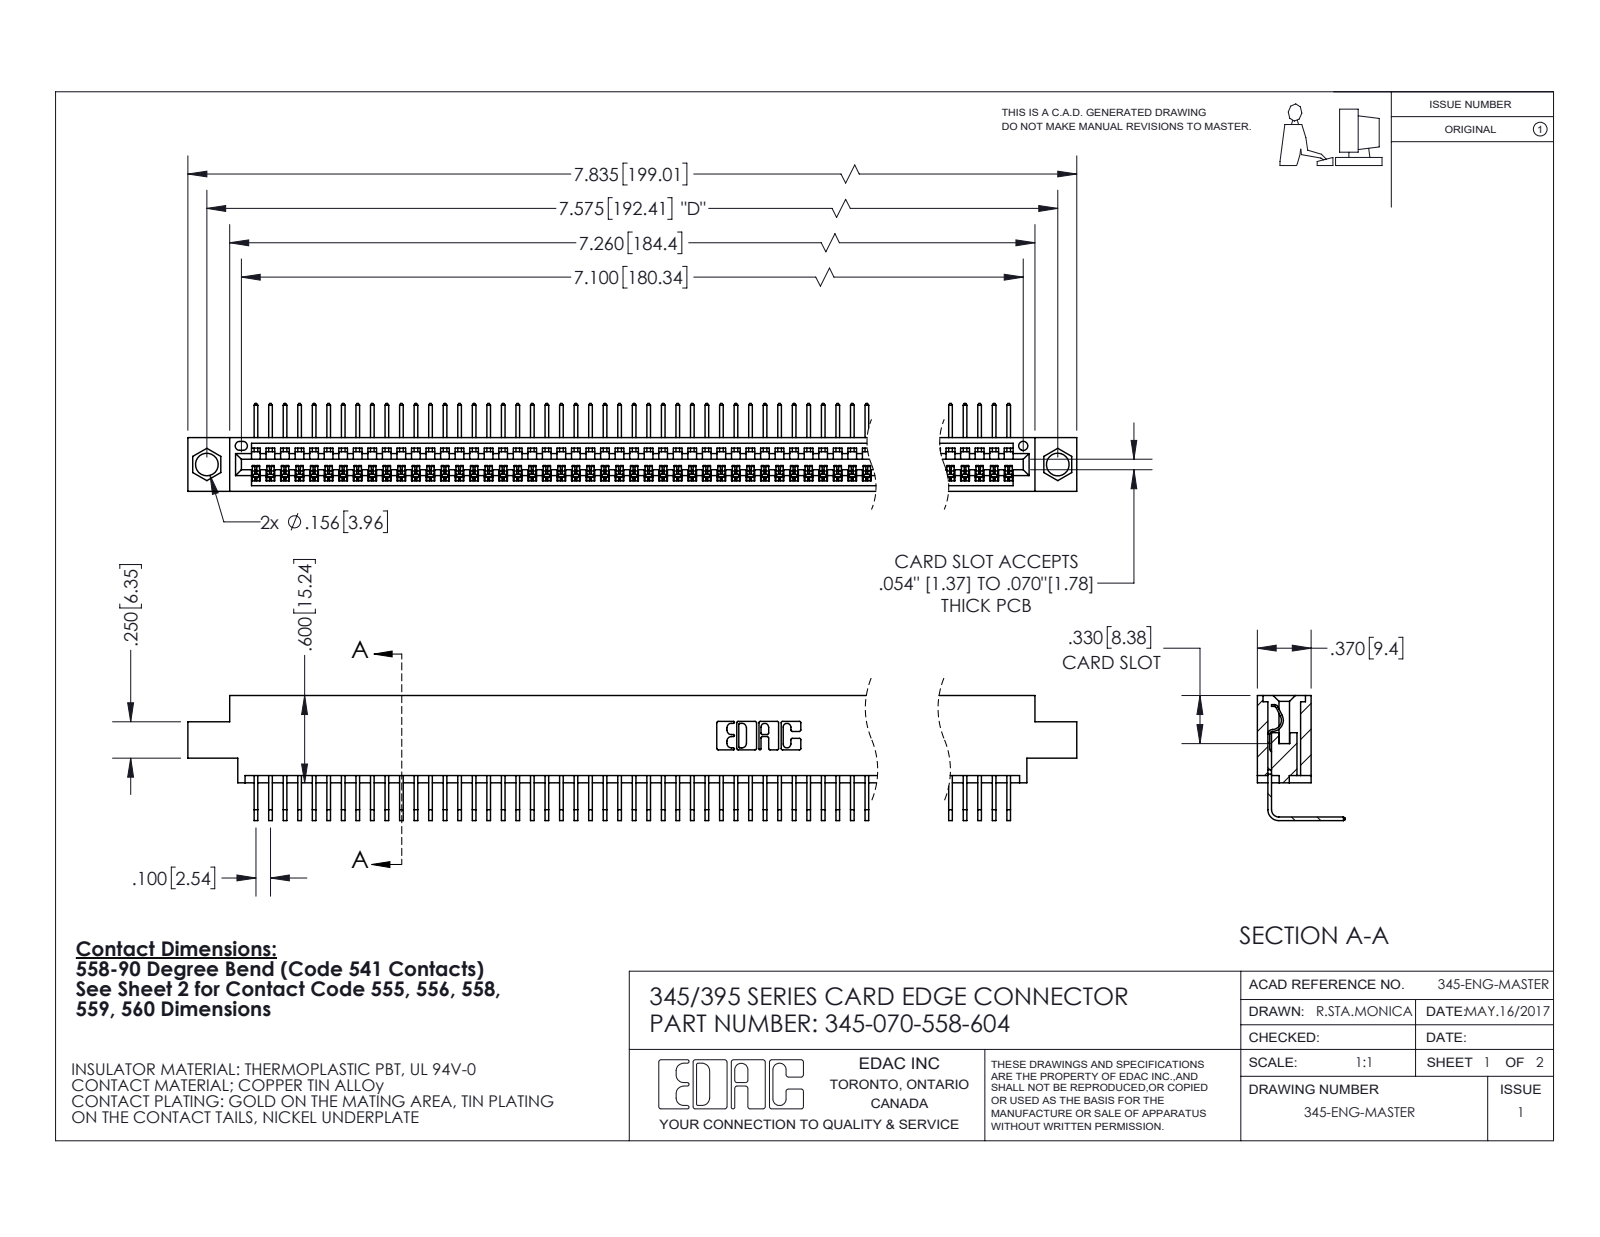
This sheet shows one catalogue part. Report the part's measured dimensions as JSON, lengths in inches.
{"part_name": "345-070-558-604; 345-292-001_558 Tail - 2; 345 Part_0.170 Offset - 0.156 Dia-TI", "step_written_by": "SolidWorks 2020 (CONFIG_CONTROL_DESIGN)", "units": "inches", "bodies": {"solids": 71, "faces": 4344, "planar": 3038, "cylindrical": 1306, "other": 0}, "overall_size": [7.835, 0.859, 0.605], "volume_in3": 1.168, "surface_area_in2": 42.1, "round_holes": [[0.156, 2], [0.064, 1]], "partial_cylinders_radius": [[0.006, 140], [0.01, 22], [0.007, 6], [0.031, 6], [0.026, 3], [0.031, 2], [0.04, 2], [0.014, 1]], "face_to_face_distances": [0.072, 0.298, 0.37, 0.2, 0.098, 0.272, 0.025, 0.225, 0.175, 0.149], "hole_center_spacings": [0.27, 7.339, 7.575]}
